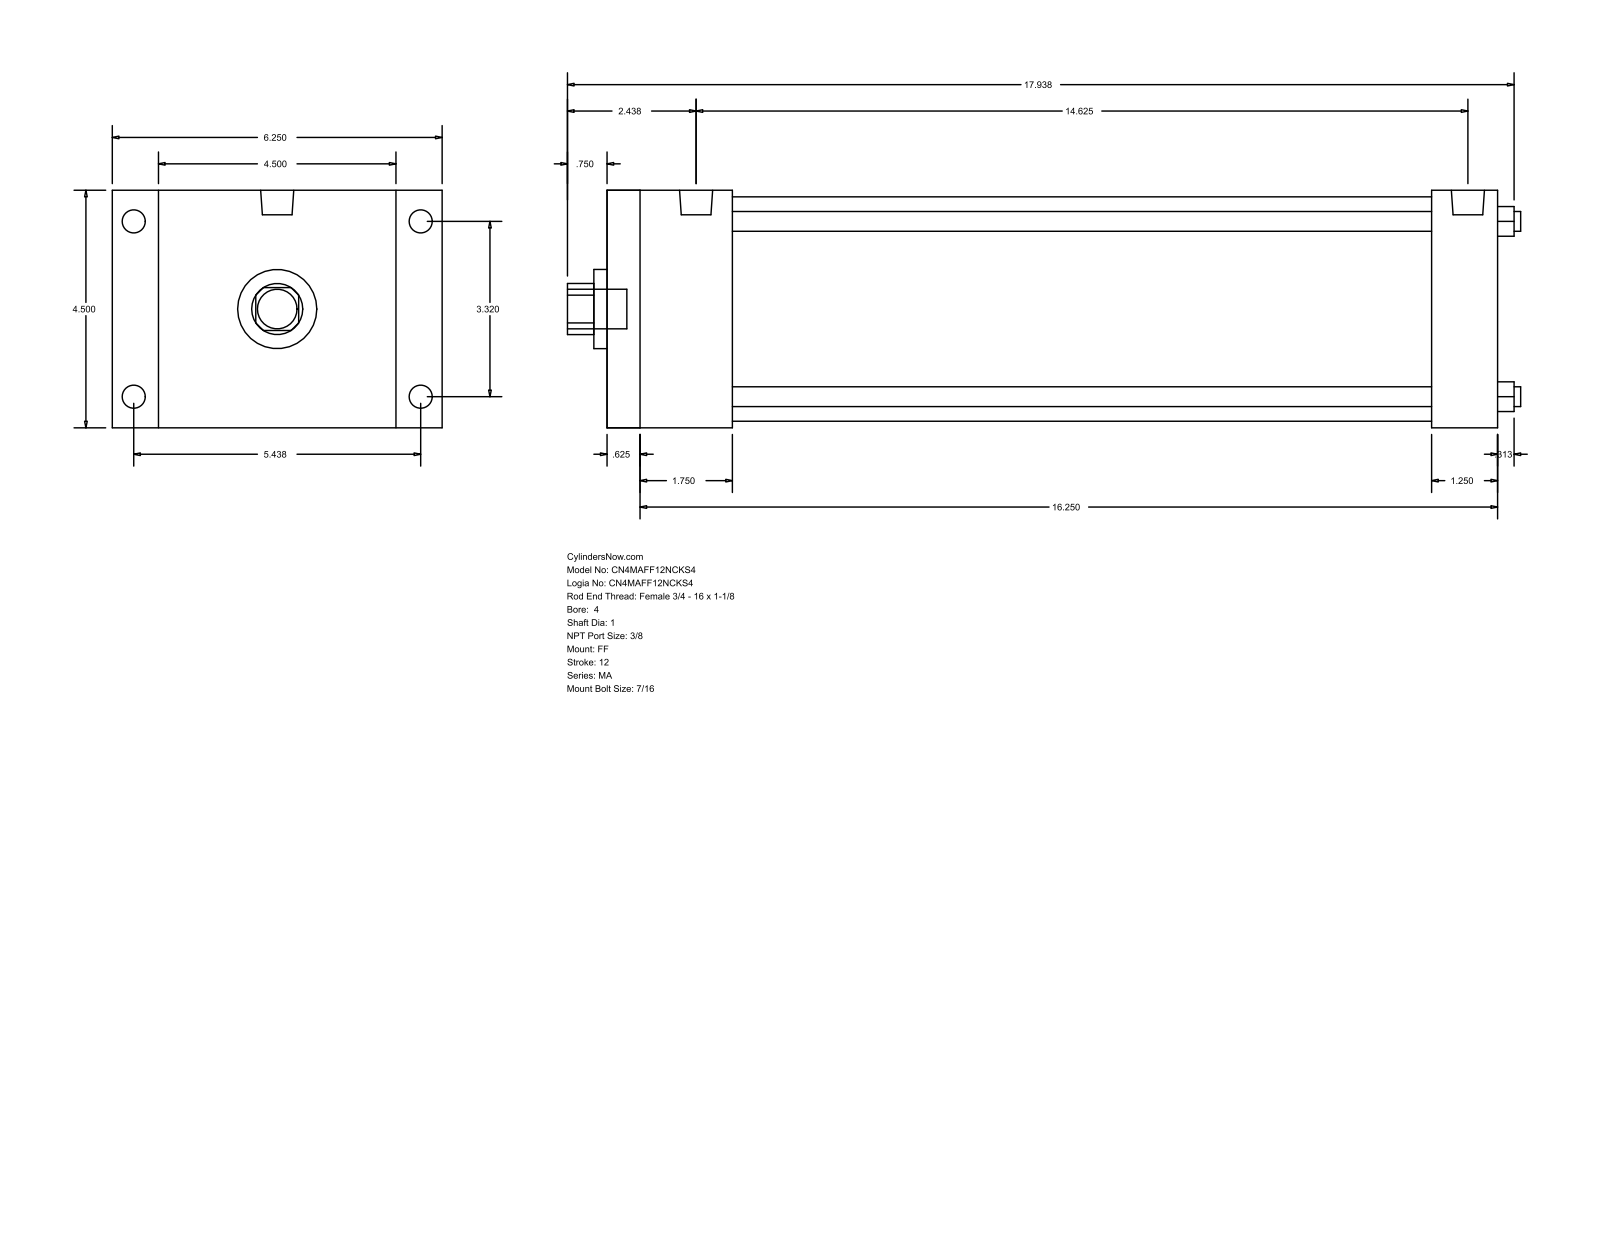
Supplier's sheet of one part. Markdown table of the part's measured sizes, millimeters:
| quantity | value |
| --- | --- |
| part name | MA_FF__0400_1 |
| STEP written by | GSSL Pune (CONFIG_CONTROL_DESIGN) |
| units | millimeters |
| bodies | 0 solids, 92 faces (64 planar, 28 cylindrical, 0 other) |
| overall size | 458.79 × 158.75 × 114.3 |
| round holes (diameter × count) | 9.53 × 4, 25.4 × 1, 38.1 × 1, 107.95 × 1 |
| round bosses / shafts (diameter × count) | 11.11 × 8, 15.93 × 2, 19.05 × 1 |
| partial cylindrical surfaces (radius × count) | 12.29 × 1 |
| main face-to-face distances | 114.3, 428.63, 15.87, 412.76, 22.23, 136.53, 396.88, 381.01, 31.75, 60.33 |
| hole center spacings | 59.62, 84.32, 119.25 |
